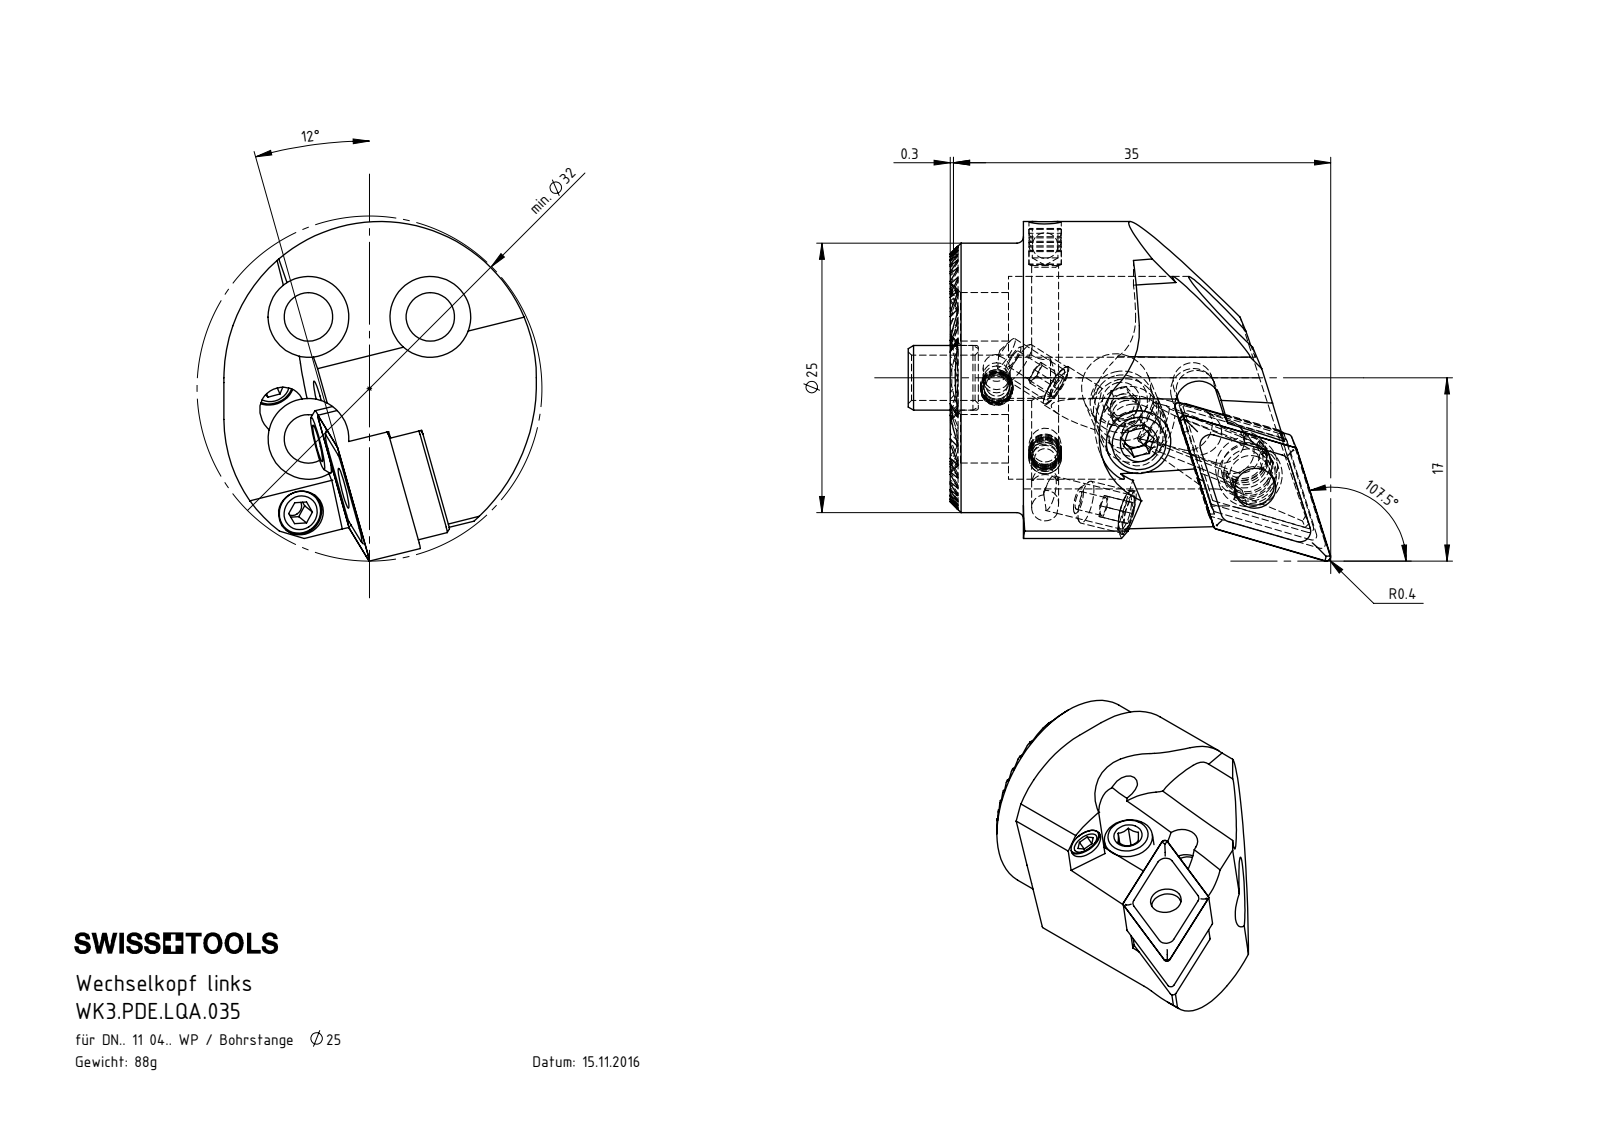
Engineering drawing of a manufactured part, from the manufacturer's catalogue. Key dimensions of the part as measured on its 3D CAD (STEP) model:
Part name (STEP PRODUCT): WKX-ER1.004.005_A_PreviewCfg; WDE-ER4.101.017_A; WK3-PDE.LQA.035_A; WDE-ER2.101.003_A (+6 more)
STEP written by: SolidWorks 2017 (AUTOMOTIVE_DESIGN)
Units: millimetres
Bodies: 15 solids, 463 faces (241 planar, 106 cylindrical, 116 other)
Overall size (bounding box): 39.21 × 31.02 × 28.92
Volume: 11 469 mm³ · Surface area: 8 467 mm²
Round holes (diameter × count): ⌀2.38 ×3, ⌀2.5 ×3, ⌀4.2 ×3, ⌀4.5 ×3, ⌀7.5 ×3, ⌀1.7 ×2, ⌀3 ×2, ⌀3.3 ×2, ⌀3.81 ×1, ⌀4.8 ×1, ⌀5 ×1, ⌀6 ×1
Round bosses / shafts (diameter × count): ⌀3 ×3, ⌀4 ×2, ⌀25 ×1, ⌀6 ×1, ⌀5.9 ×1, ⌀2.87 ×1
Partial cylindrical surfaces — rounded edges, fillets, slot ends (radius × count): R0.12 ×20, R0.4 ×8, R2.1 ×5, R7 ×2, R13 ×2, R1.83 ×1, R1.85 ×1, R2.25 ×1
Main face-to-face distances: 4.33, 1.08, 3.25, 5.41, 7.58, 8.66, 2.16, 2.17, 9.74, 6.5
Hole centre spacings: 8, 11.32, 11.81, 16.01
